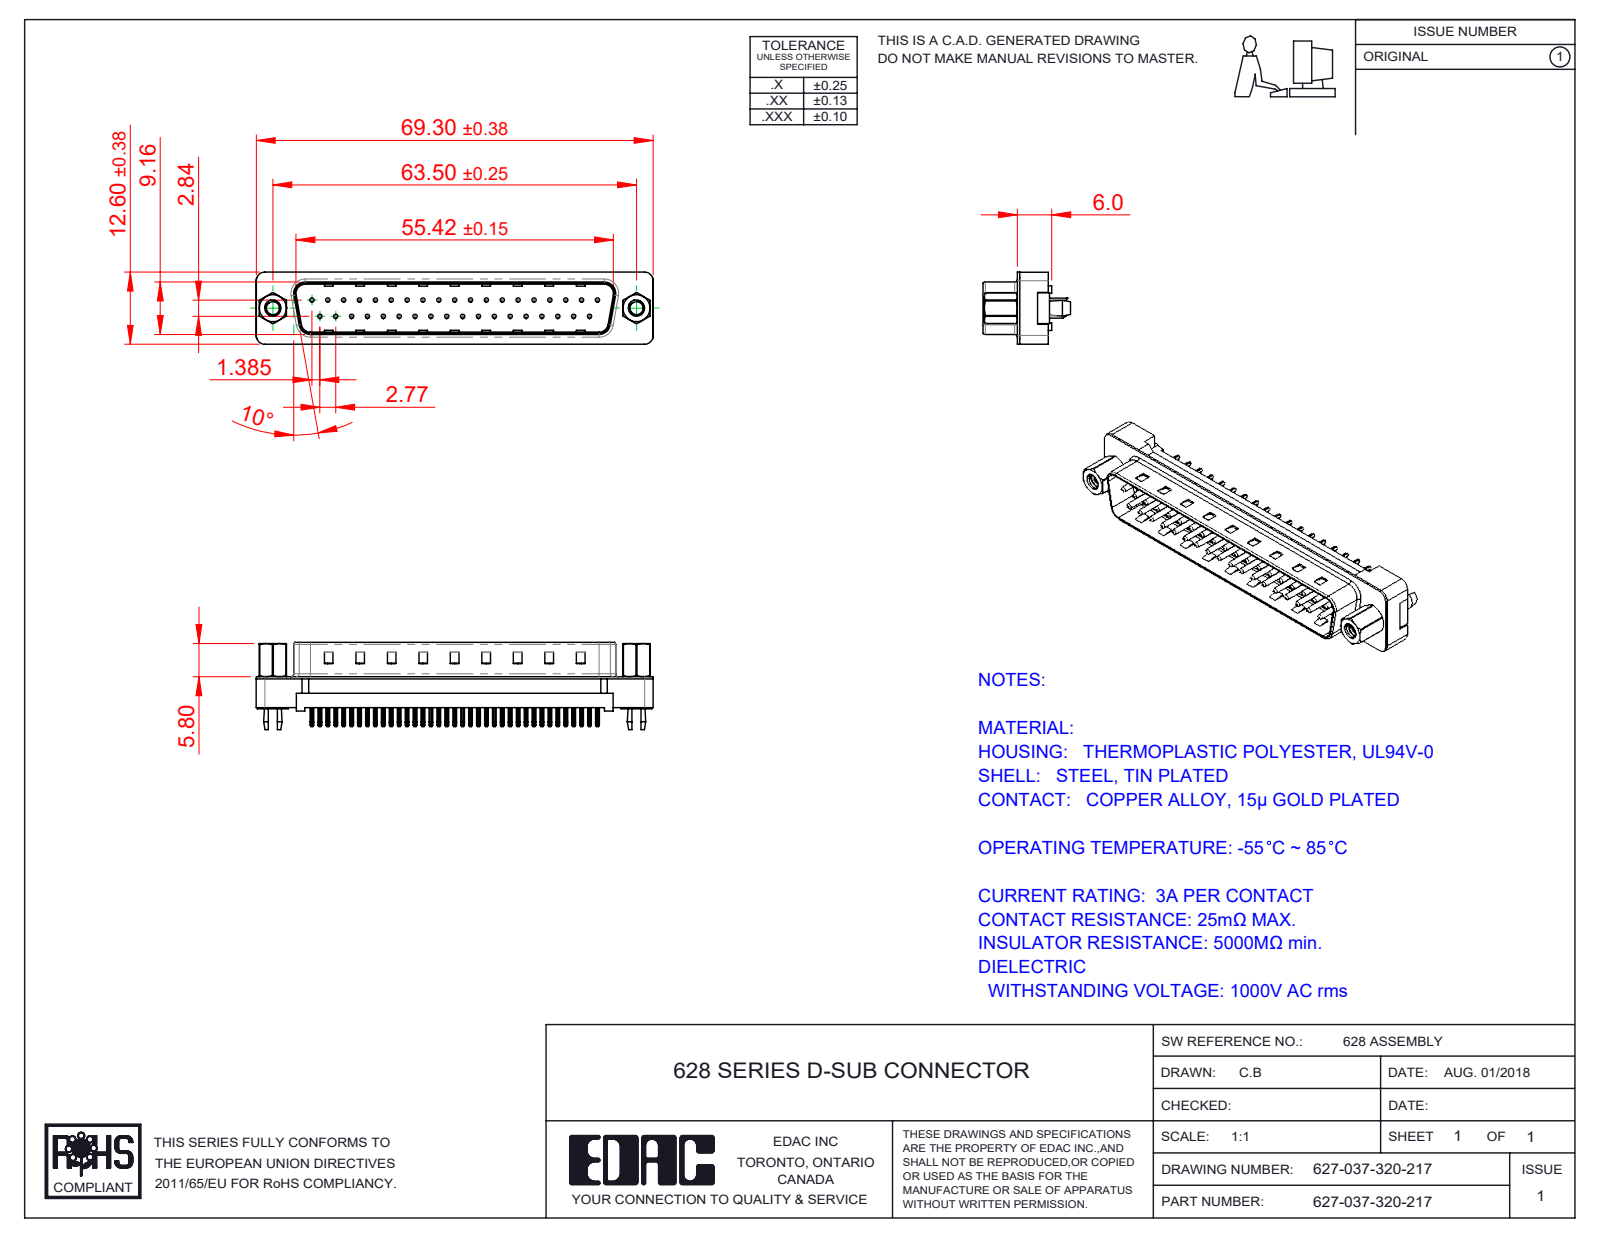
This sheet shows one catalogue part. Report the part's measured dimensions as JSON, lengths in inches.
{"part_name": "627 PB Contact Row 1_20; 627 Plastic Body Housing_37 Contacts; 627 PB Shell_37 Contacts; 627 4-40 Hex Standoff (+3 more)", "step_written_by": "SolidWorks 2020 (CONFIG_CONTROL_DESIGN)", "units": "inches", "bodies": {"solids": 43, "faces": 2629, "planar": 1673, "cylindrical": 766, "other": 190}, "overall_size": [2.729, 0.6, 0.496], "volume_in3": 0.21, "surface_area_in2": 12.6, "round_holes": [[0.014, 37], [0.033, 37], [0.089, 2], [0.09, 2], [0.157, 2], [0.189, 2], [0.197, 2]], "round_bosses_or_shafts": [[0.03, 37], [0.193, 2], [0.11, 2]], "partial_cylinders_radius": [[0.01, 74], [0.005, 37], [0.02, 8], [0.059, 8], [0.035, 4], [0.063, 4], [0.079, 4], [0.016, 2]], "face_to_face_distances": [0.016, 0.098, 0.345, 0.114, 0.062, 0.256, 0.213, 0.027, 0.334, 0.318], "hole_center_spacings": [0.109, 0.218, 0.124, 0.327, 0.436, 0.545, 0.654, 0.763]}
